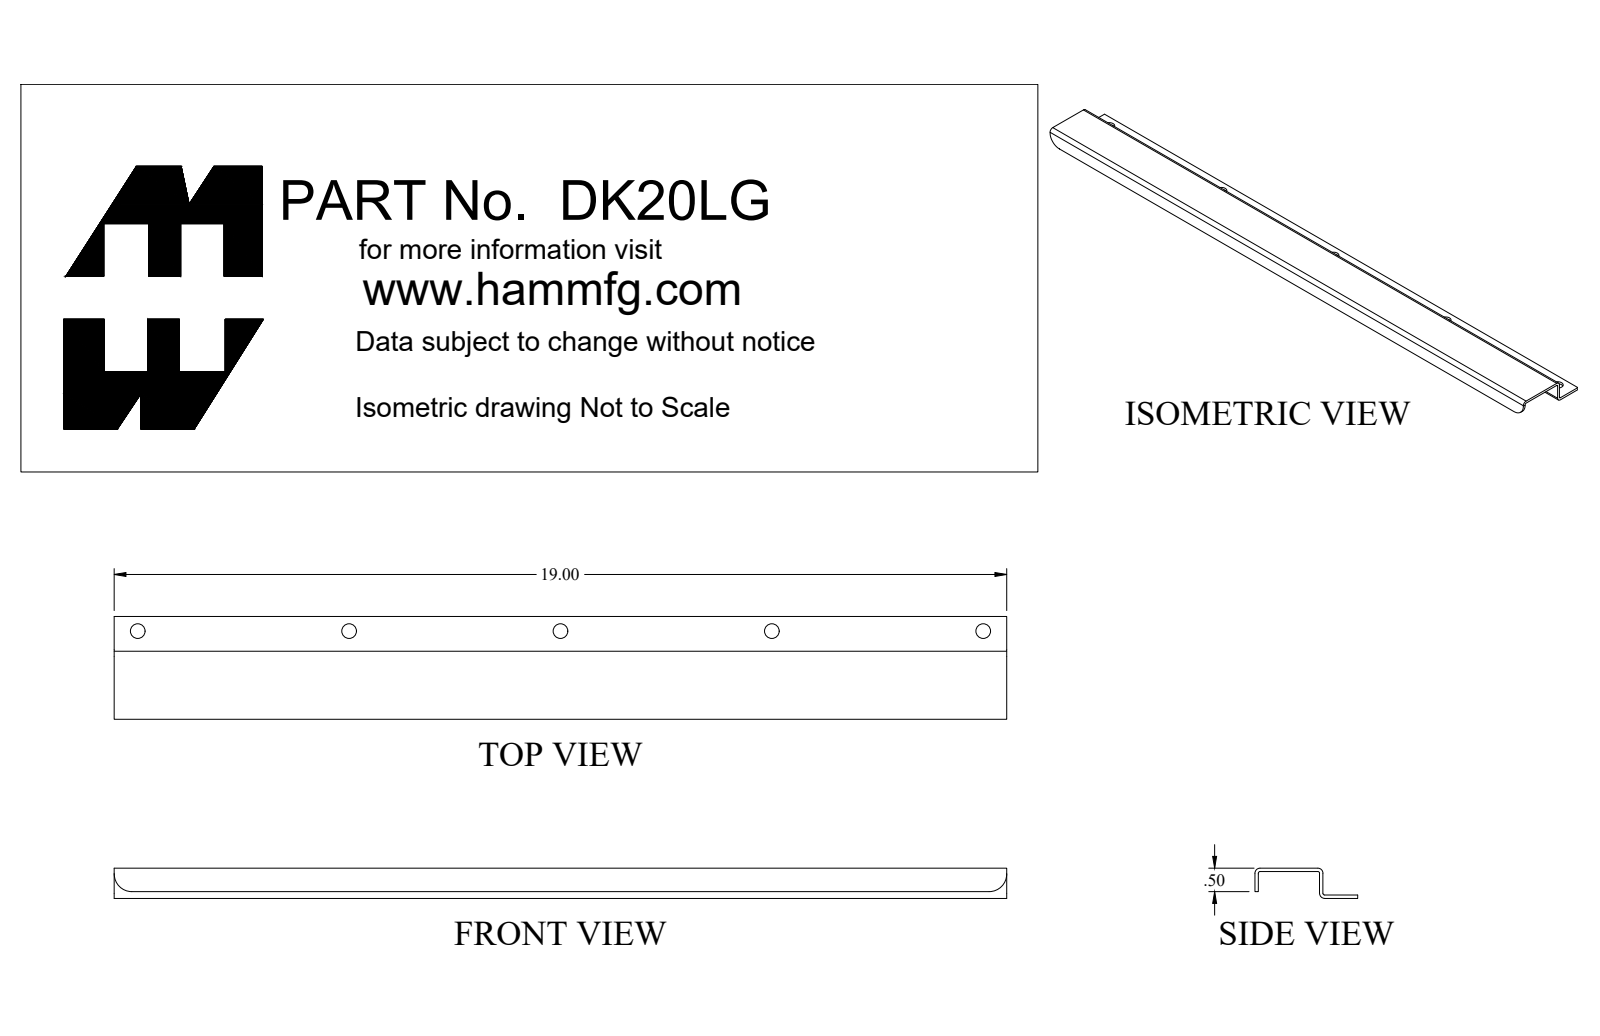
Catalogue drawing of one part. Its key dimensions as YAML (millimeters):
part_name: "DK20LG_Default"
step_written_by: "SolidWorks 2018 (CONFIG_CONTROL_DESIGN)"
units: millimeters
bodies: {solids: 5, faces: 69, planar: 35, cylindrical: 28, other: 6}
overall_size: [482.6, 55.6, 33.6]
volume: 85410
surface_area: 99290
round_holes:
  - {diameter: 8, count: 5}
  - {diameter: 5.1, count: 1}
  - {diameter: 7, count: 1}
round_bosses_or_shafts:
  - {diameter: 15.9, count: 1}
  - {diameter: 12.3, count: 1}
  - {diameter: 6.4, count: 1}
partial_cylinders:
  - {radius: 0.9, count: 3}
  - {radius: 2.7, count: 3}
  - {radius: 9.5, count: 2}
face_to_face_distances: [1.8, 14.5, 16.4, 35, 12.7, 1.6, 16.1, 18, 3.4, 36.8]
hole_center_spacings: [114.3, 228.6, 342.9, 457.2]
